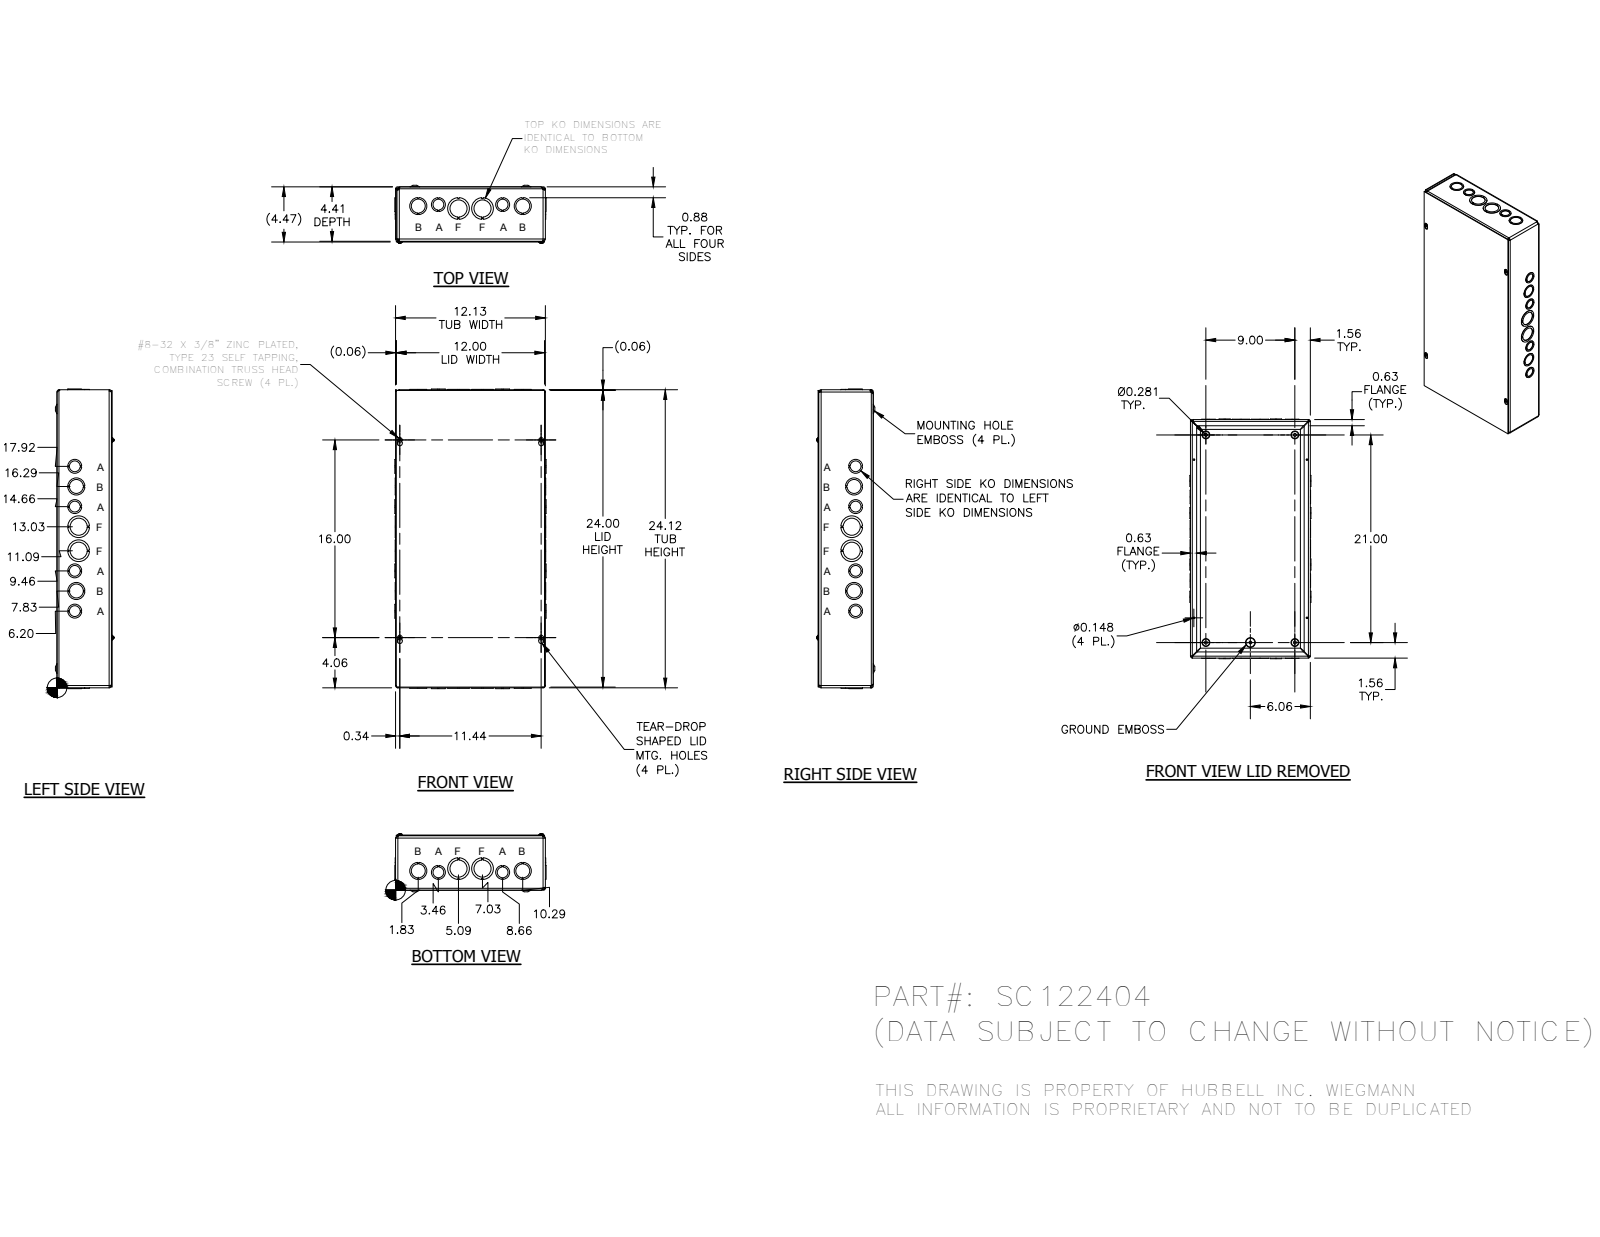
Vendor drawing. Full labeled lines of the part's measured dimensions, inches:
Part name (STEP PRODUCT): SC1224BKP; SC122404WRA; SC1224LID; 34056 (+1 more)
STEP written by: Autodesk Inventor 2014 (AUTOMOTIVE_DESIGN)
Units: inches
Bodies: 30 solids, 1142 faces (749 planar, 235 cylindrical, 158 other)
Overall size (bounding box): 24.249 × 12.249 × 4.693
Round holes (diameter × count): ⌀1.125 ×10, ⌀1.375 ×8, ⌀0.875 ×6, ⌀0.148 ×4, ⌀0.3 ×4, ⌀1.75 ×4, ⌀0.165 ×1
Round bosses / shafts (diameter × count): ⌀0.384 ×4, ⌀0.164 ×4, ⌀0.228 ×1
Partial cylindrical surfaces — rounded edges, fillets, slot ends (radius × count): R0.125 ×12, R0.187 ×8, R0.055 ×4, R0.062 ×4, R0.094 ×4, R0.117 ×4, R0.124 ×4, R0.156 ×4
Main face-to-face distances: 0.062, 4.343, 4.405, 0.063, 4.406, 4.468, 0.062, 12.125, 12.063, 12.063
Hole centre spacings: 1.635, 1.659, 3.265, 3.584, 5.204, 6.831, 18.54, 21.135
